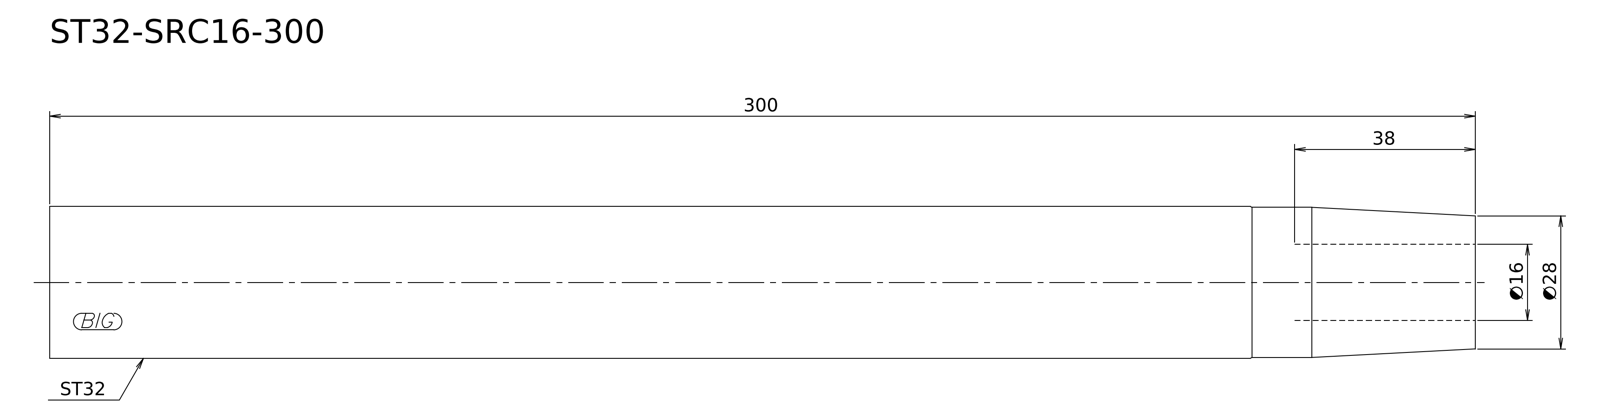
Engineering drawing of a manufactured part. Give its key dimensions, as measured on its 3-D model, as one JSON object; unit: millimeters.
{"step_written_by": "Kubotek KeyCreator V8.5.1 (14335) (CONFIG_CONTROL_DESIGN)", "units": "millimeters", "bodies": {"solids": 1, "faces": 6, "planar": 2, "cylindrical": 2, "other": 2}, "overall_size": [300, 32, 32], "volume_mm3": 237380, "surface_area_mm2": 31336, "round_bosses_or_shafts": [[32, 1], [31.6, 1]], "face_to_face_distances": [300]}
